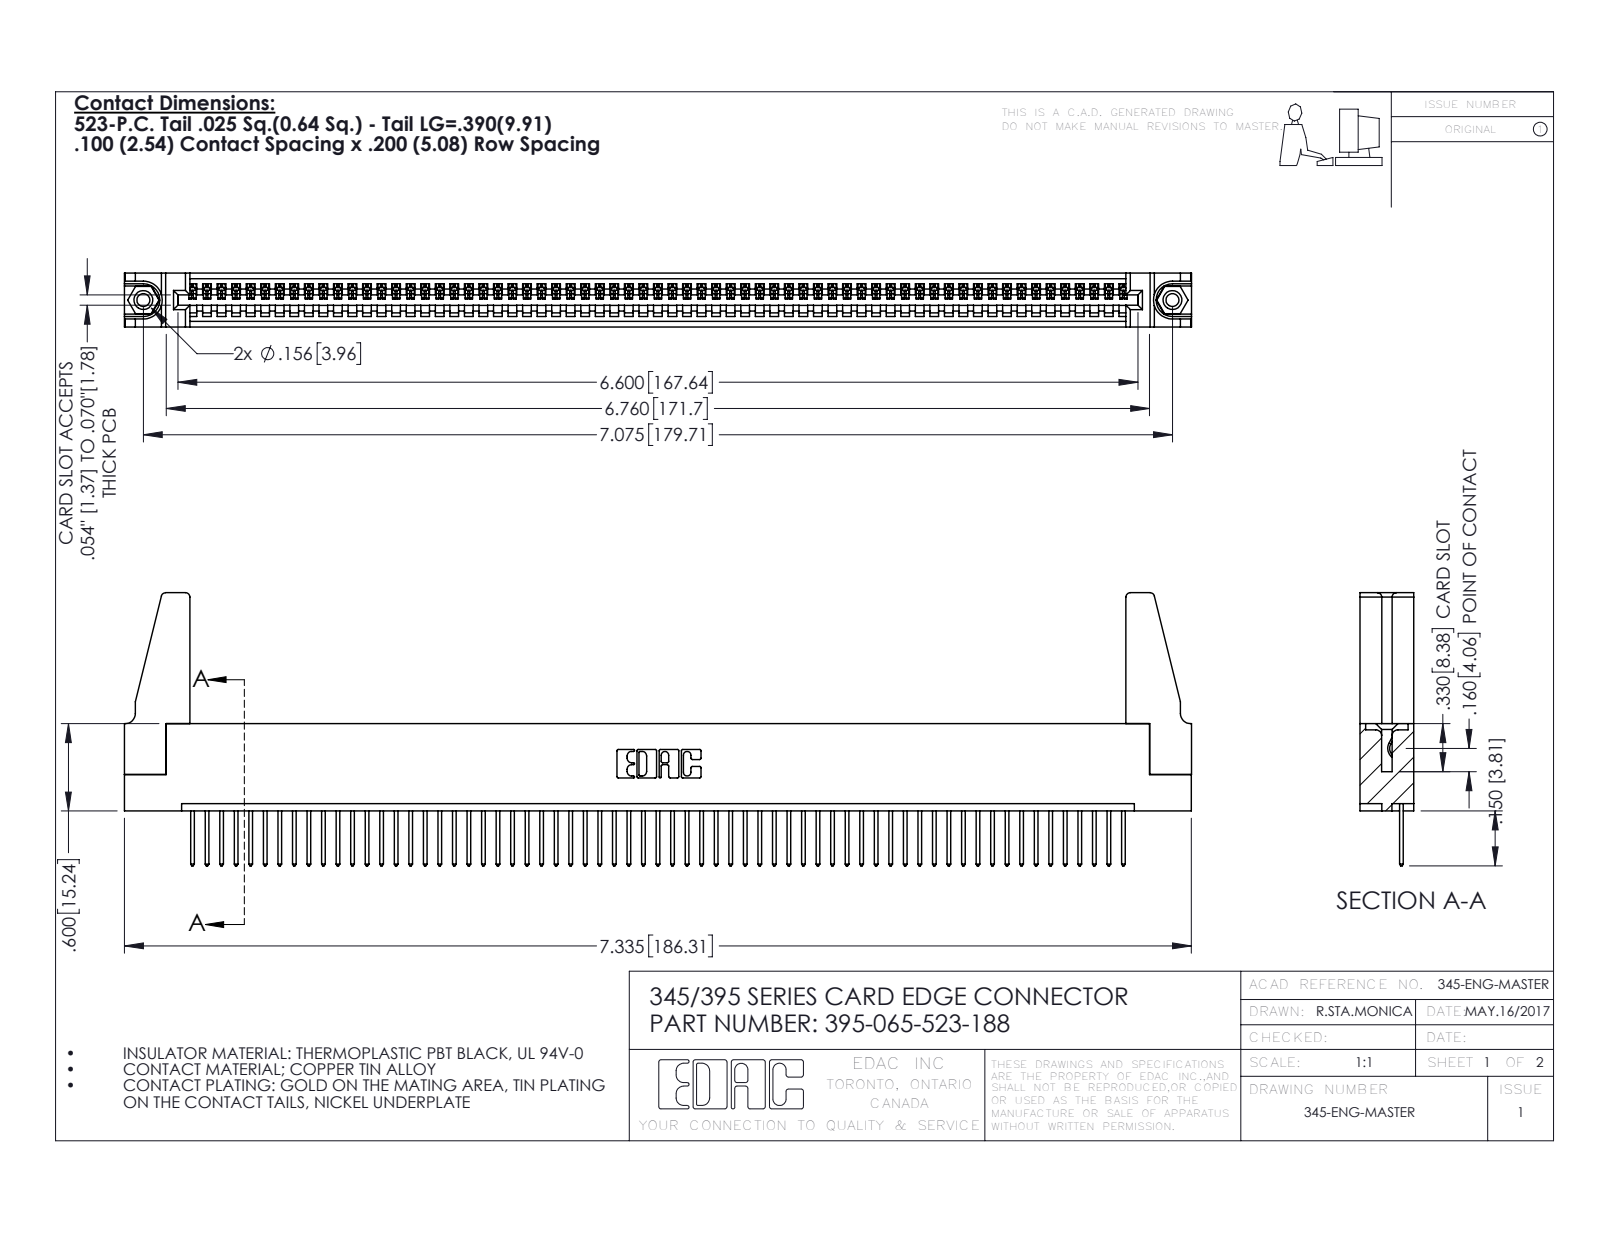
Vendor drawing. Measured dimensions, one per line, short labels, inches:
name: 345-292-001_345-293-123; 345 Part_Flush Mounting Lugs - 0.156 Dia-TH; 345-220-078_345-220-088; 395-065-523-188 (+1 more)
written by: SolidWorks 2016 (CONFIG_CONTROL_DESIGN)
unit: in
bodies: 70 solids, 4020 faces (2752 planar, 1252 cylindrical, 16 other)
size: 7.336 × 1.877 × 0.37
volume: 1.288 in³; area: 42.24 in²
holes: 2× ⌀0.089, 2× ⌀0.125, 2× ⌀0.156, 1× ⌀0.064
bosses: 2× ⌀0.155
rounds: 130× R0.006, 130× R0.01, 22× R0.01, 8× R0.03, 6× R0.007, 6× R0.031, 3× R0.026, 2× R0.031
face distances: 0.072, 0.298, 0.37, 0.2, 0.098, 0.272, 0.025, 0.225, 0.149, 0.072
hole spacings: 0.27, 6.839, 7.075
